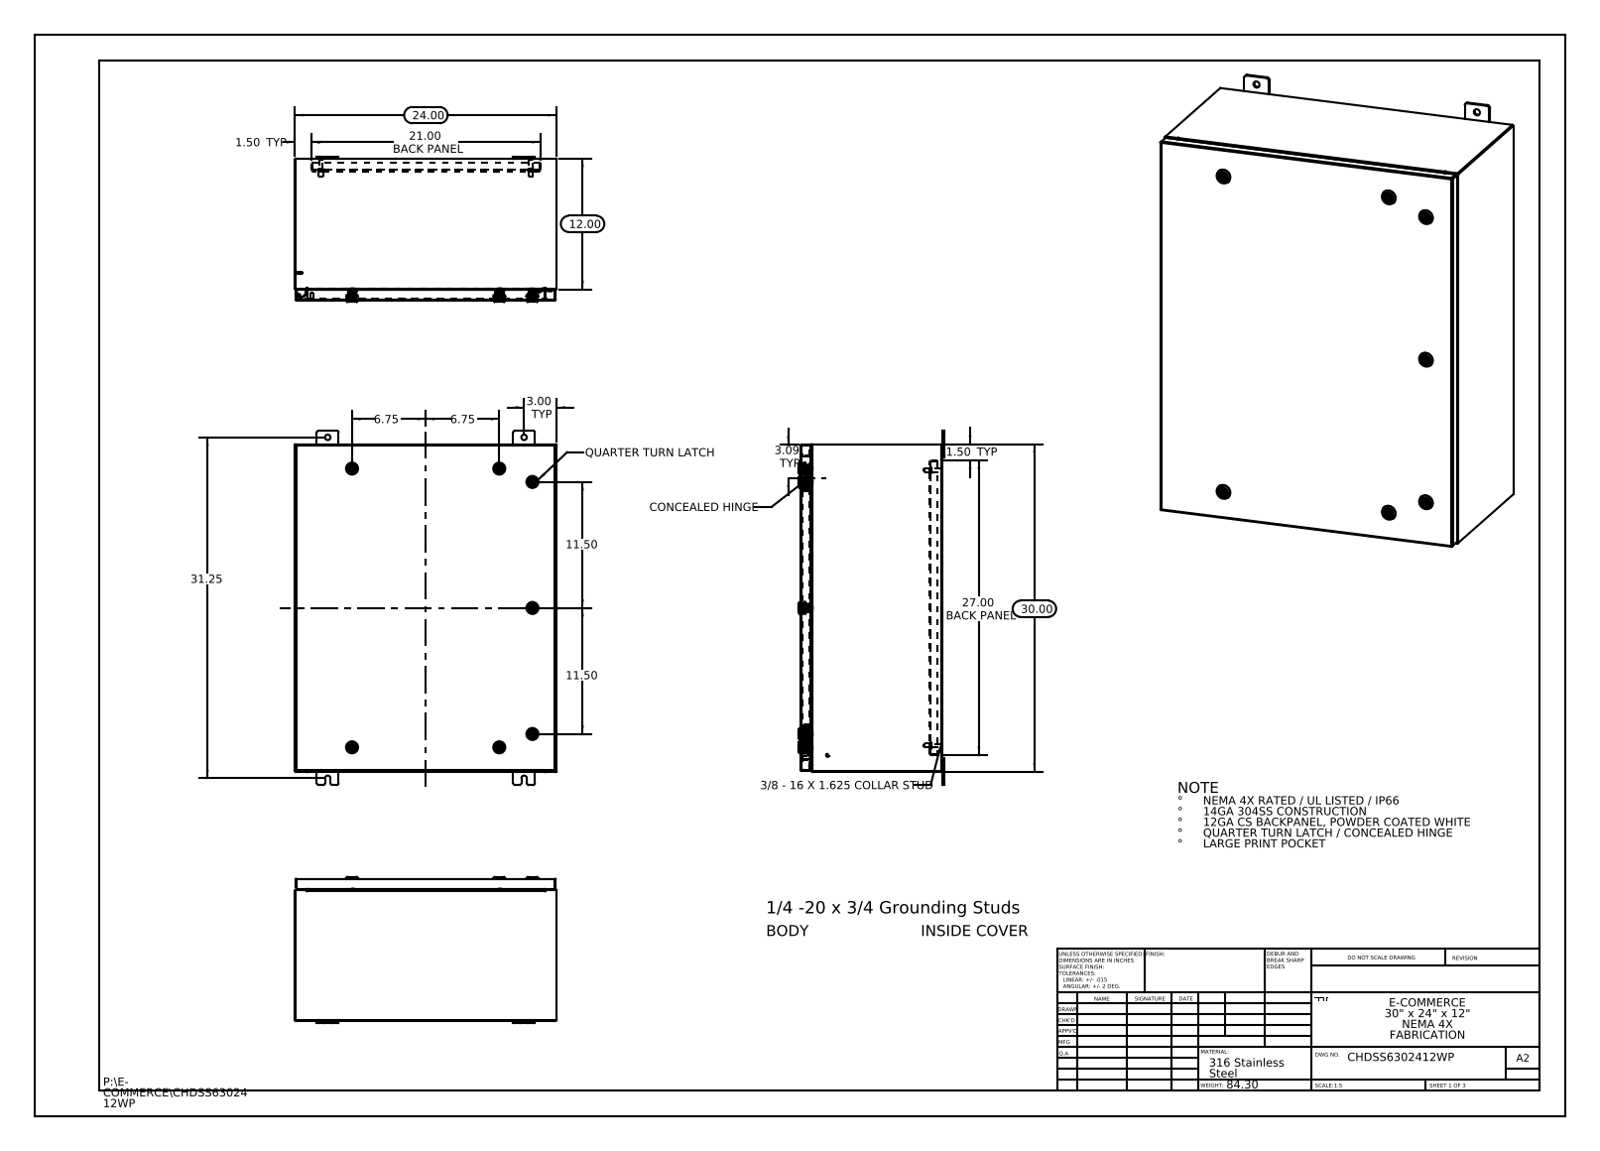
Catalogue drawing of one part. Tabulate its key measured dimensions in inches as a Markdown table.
| quantity | value |
| --- | --- |
| part name | Housing-211301-IB-Industrilas_Housing-211301-IB-Industrilas; Nut-211301-IB-Industrilas_Nut-211301-IB-Industrilas; Washer-221320-IB-Industrilas_Washer-221320-IB-Industrilas; Insert-221320-IB-Industrilas_Insert-221320-IB-Industrilas (+8 more) |
| STEP written by | SolidWorks 2013 (CONFIG_CONTROL_DESIGN) |
| units | inches |
| bodies | 61 solids, 6252 faces (1822 planar, 1948 cylindrical, 2482 other) |
| overall size | 32.5 × 24 × 13.356 |
| volume | 299.1 in³ |
| surface area | 7 484 in² |
| round holes (diameter × count) | 0.5 × 8, 0.197 × 7, 0.394 × 7, 0.4 × 7, 0.63 × 7, 0.787 × 7, 0.136 × 4, 0.211 × 1 |
| round bosses / shafts (diameter × count) | 0.236 × 9, 1.102 × 7, 0.78 × 7, 0.626 × 7, 0.61 × 7, 0.531 × 7, 0.392 × 7, 0.114 × 7 |
| partial cylindrical surfaces (radius × count) | 0.006 × 231, 0.118 × 231, 0.028 × 84, 0.02 × 28, 0.197 × 28, 0.19 × 24, 0.013 × 22, 0.088 × 18 |
| main face-to-face distances | 0.075, 0.074, 23.925, 13.01, 12.935, 12.936, 12.861, 0.104, 1, 29.925 |
| hole center spacings | 0.688, 1.858, 3.276, 11.55, 13.5, 16.583, 18, 19.25 |
